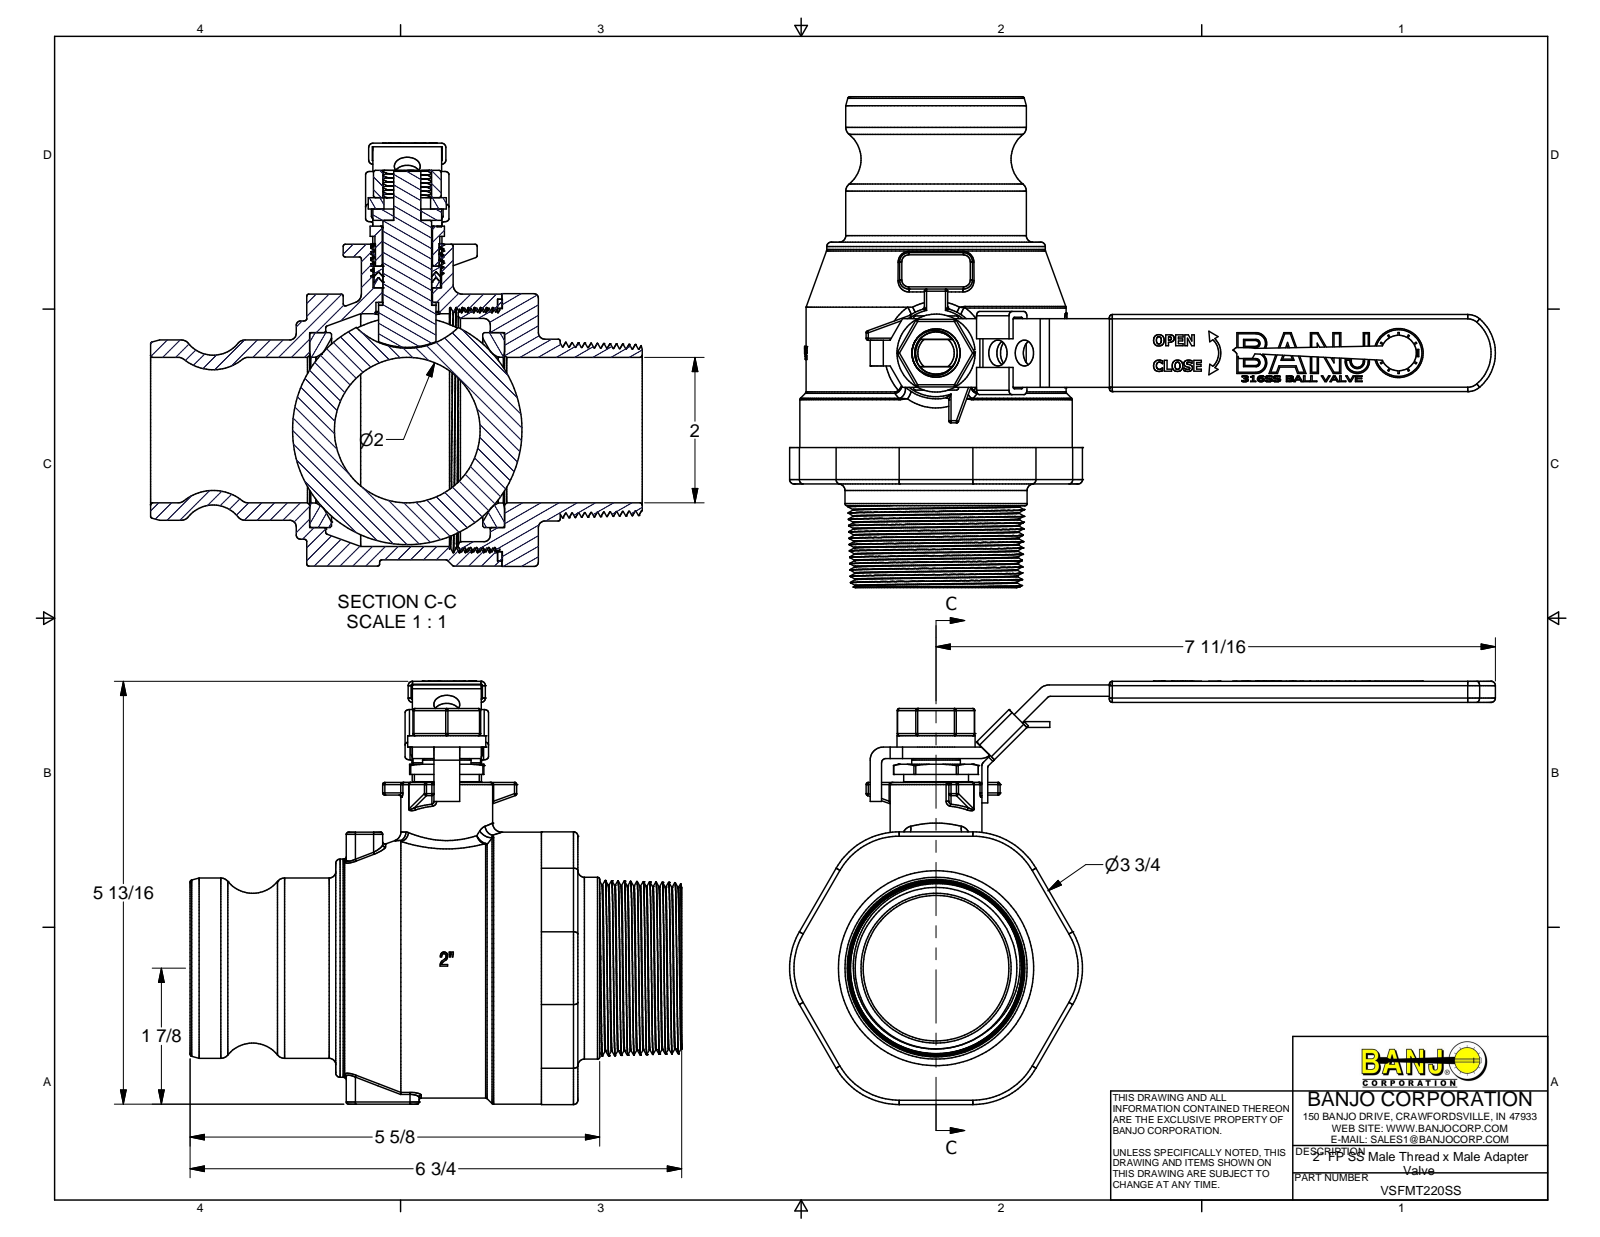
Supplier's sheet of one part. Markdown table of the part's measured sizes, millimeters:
| quantity | value |
| --- | --- |
| part name | VSFMT220SS; VSSF25254; VSS15020; VSS15021 (+8 more) |
| STEP written by | Autodesk Inventor 2013 (AUTOMOTIVE_DESIGN) |
| units | millimeters |
| bodies | 19 solids, 1640 faces (803 planar, 326 cylindrical, 511 other) |
| overall size | 246.1 × 171.5 × 147.9 |
| volume | 474 900 mm³ |
| surface area | 201 700 mm² |
| round holes (diameter × count) | 9 × 2, 50.8 × 2, 4.6 × 1, 6.5 × 1, 10 × 1, 14.7 × 1, 16.3 × 1, 16.3 × 1, 16.8 × 1, 17 × 1, 17.2 × 1, 17.5 × 1 |
| round bosses / shafts (diameter × count) | 95 × 1, 90.7 × 1, 85.1 × 1, 82 × 1, 76.2 × 1, 68.1 × 1, 63.5 × 1, 63 × 1 |
| partial cylindrical surfaces (radius × count) | 0.8 × 84, 1.5 × 21, 1 × 8, 25.4 × 7, 3.2 × 6, 3.8 × 4, 4.6 × 3, 6.4 × 3 |
| main face-to-face distances | 1.3, 6.1, 4, 2.1, 0.8, 4.8, 67.9, 79.8, 11.8, 7.4 |
| hole center spacings | 11.1, 13.1, 161.3 |
